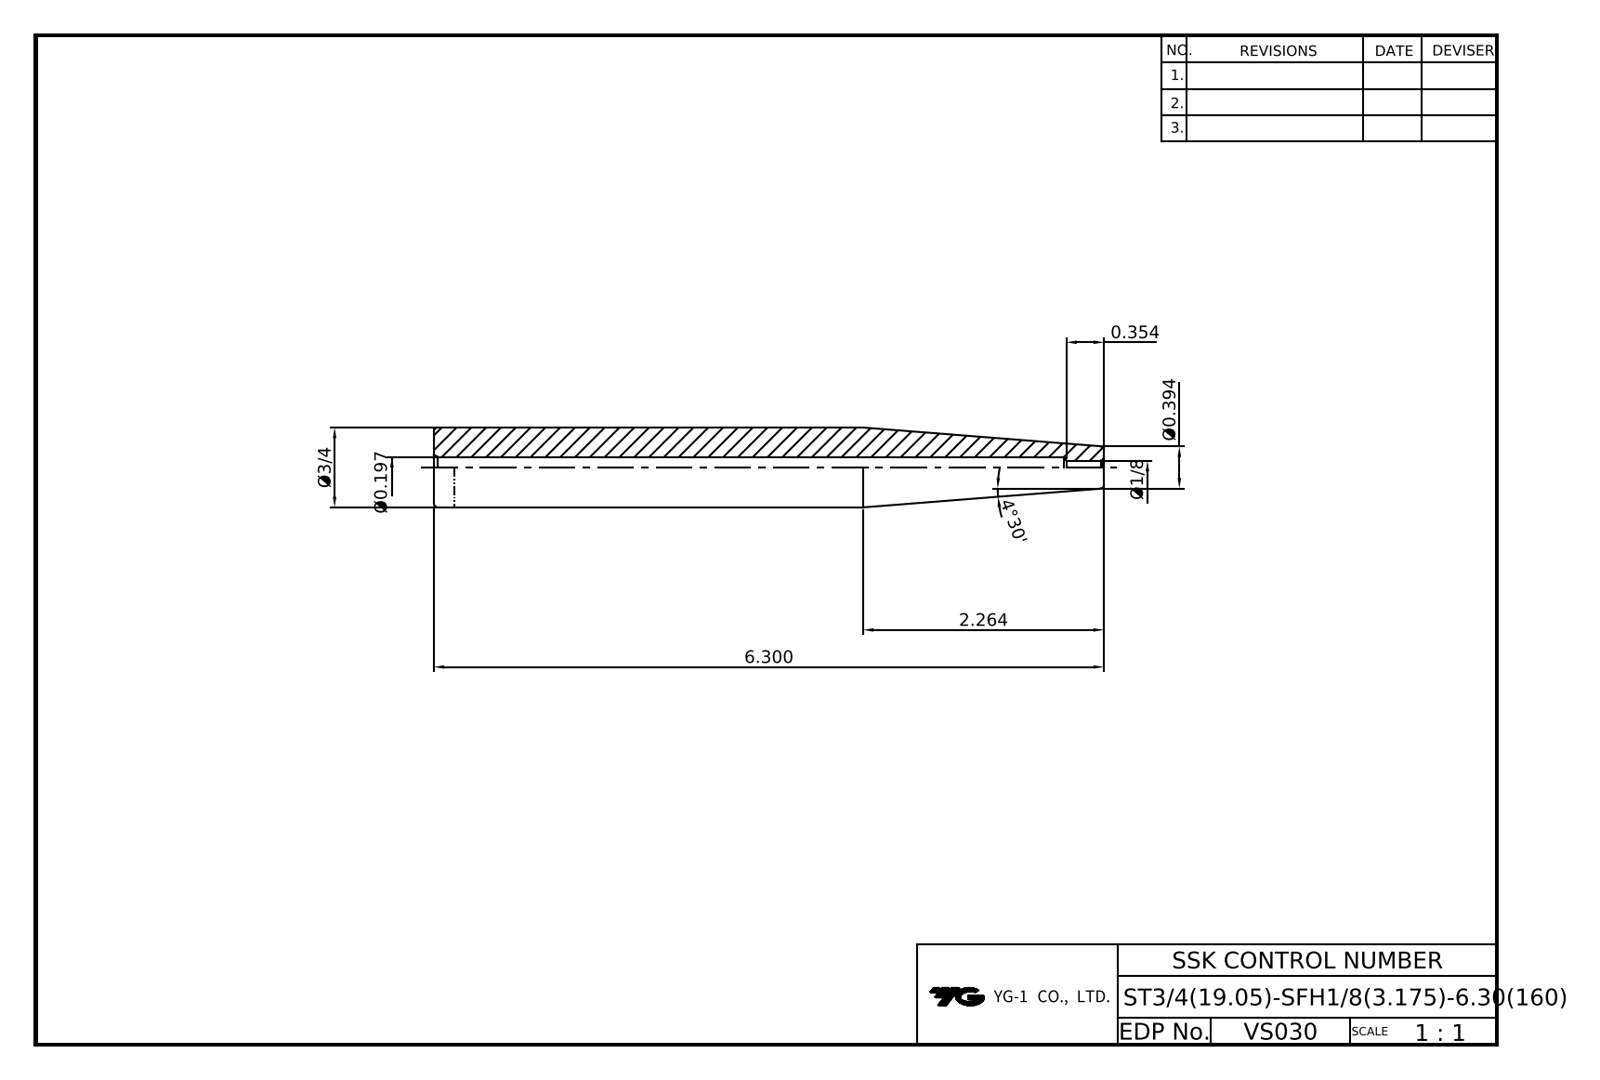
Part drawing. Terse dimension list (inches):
name: LO-ST19.05-SFH3.175-160
written by: Autodesk Inventor 2024 (AUTOMOTIVE_DESIGN)
unit: in
bodies: 1 solid, 10 faces (2 planar, 3 cylindrical, 5 other)
size: 6.299 × 0.75 × 0.75
volume: 2.197 in³; area: 17.87 in²
holes: 1× ⌀0.125, 1× ⌀0.197
bosses: 1× ⌀0.75
face distances: 6.299
